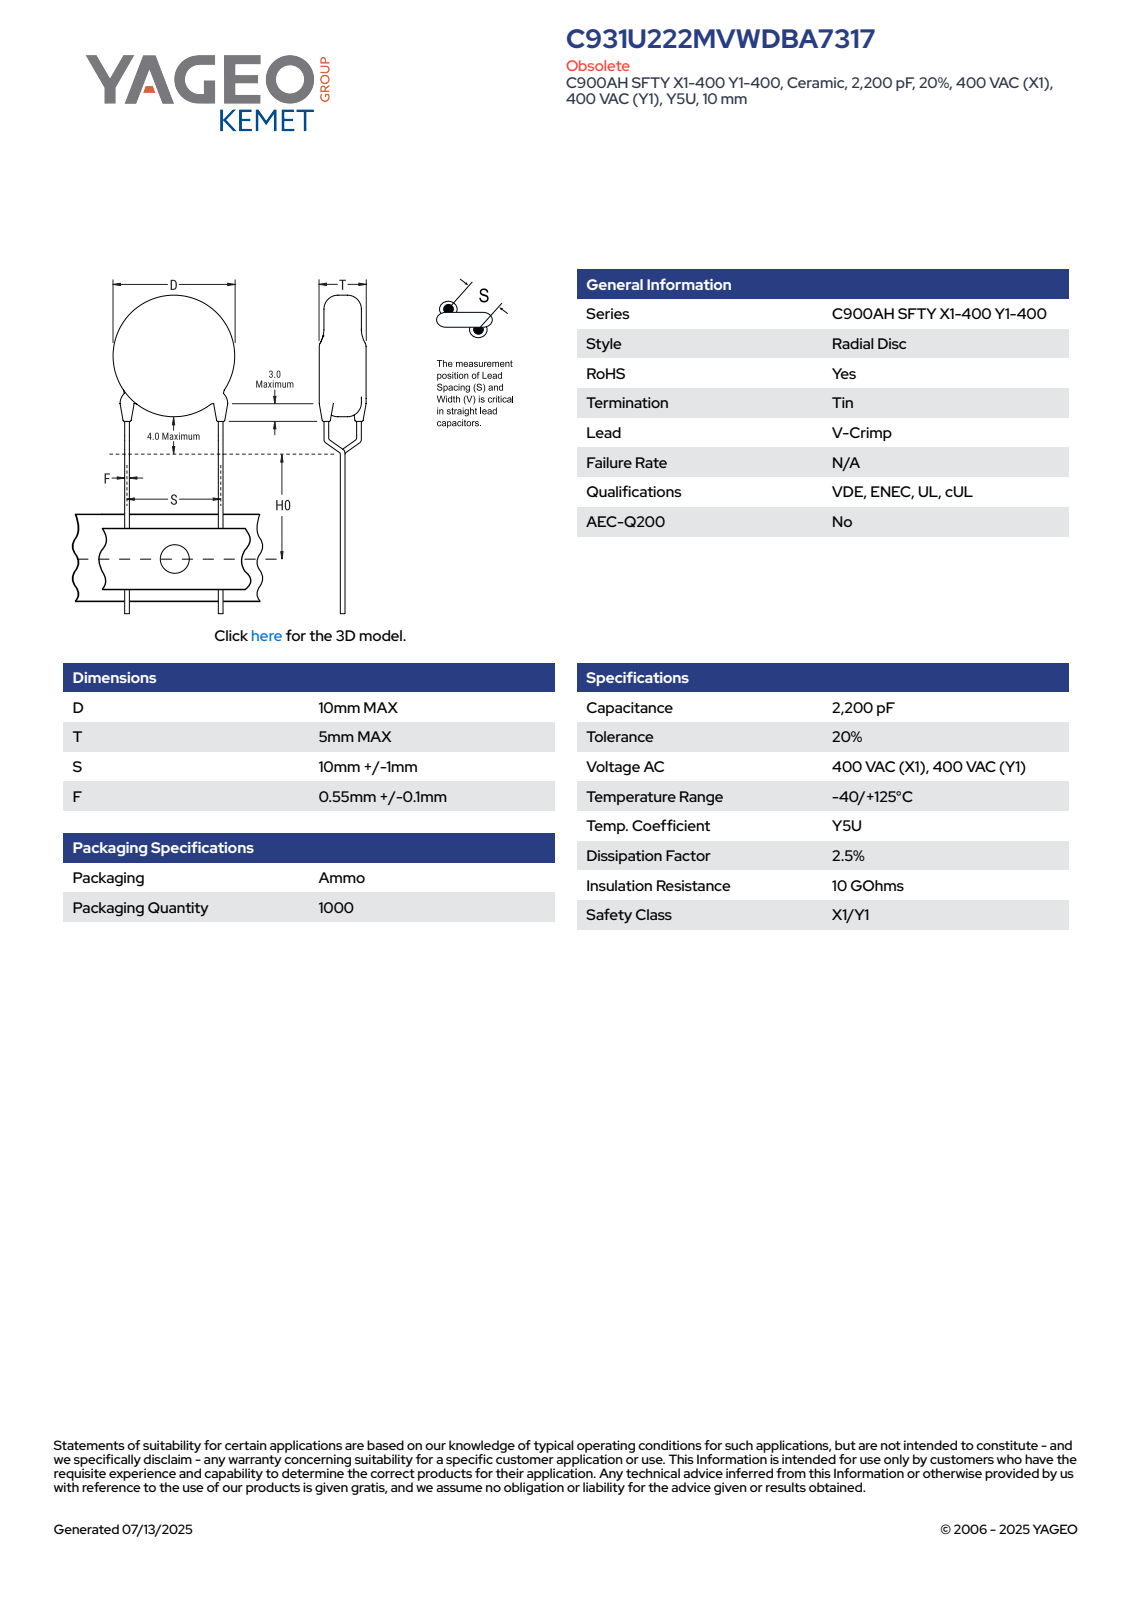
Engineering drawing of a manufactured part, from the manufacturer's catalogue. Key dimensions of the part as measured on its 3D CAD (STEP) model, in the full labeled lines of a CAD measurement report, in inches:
Part name (STEP PRODUCT): CCD_VCC900_D10T5S10LL20F0.65
STEP written by: SolidWorks 2014 (AUTOMOTIVE_DESIGN)
Units: inches
Bodies: 5 solids, 93 faces (65 planar, 16 cylindrical, 12 other)
Overall size (bounding box): 1.331 × 0.419 × 0.197
Volume: 0.024 in³ · Surface area: 0.634 in²
Round bosses / shafts (diameter × count): ⌀0.026 ×6, ⌀0.394 ×1
Main face-to-face distances: 0.197, 0.902, 0.051, 1.159, 0.258, 1.108, 0.207, 0.013, 0.041, 0.106
